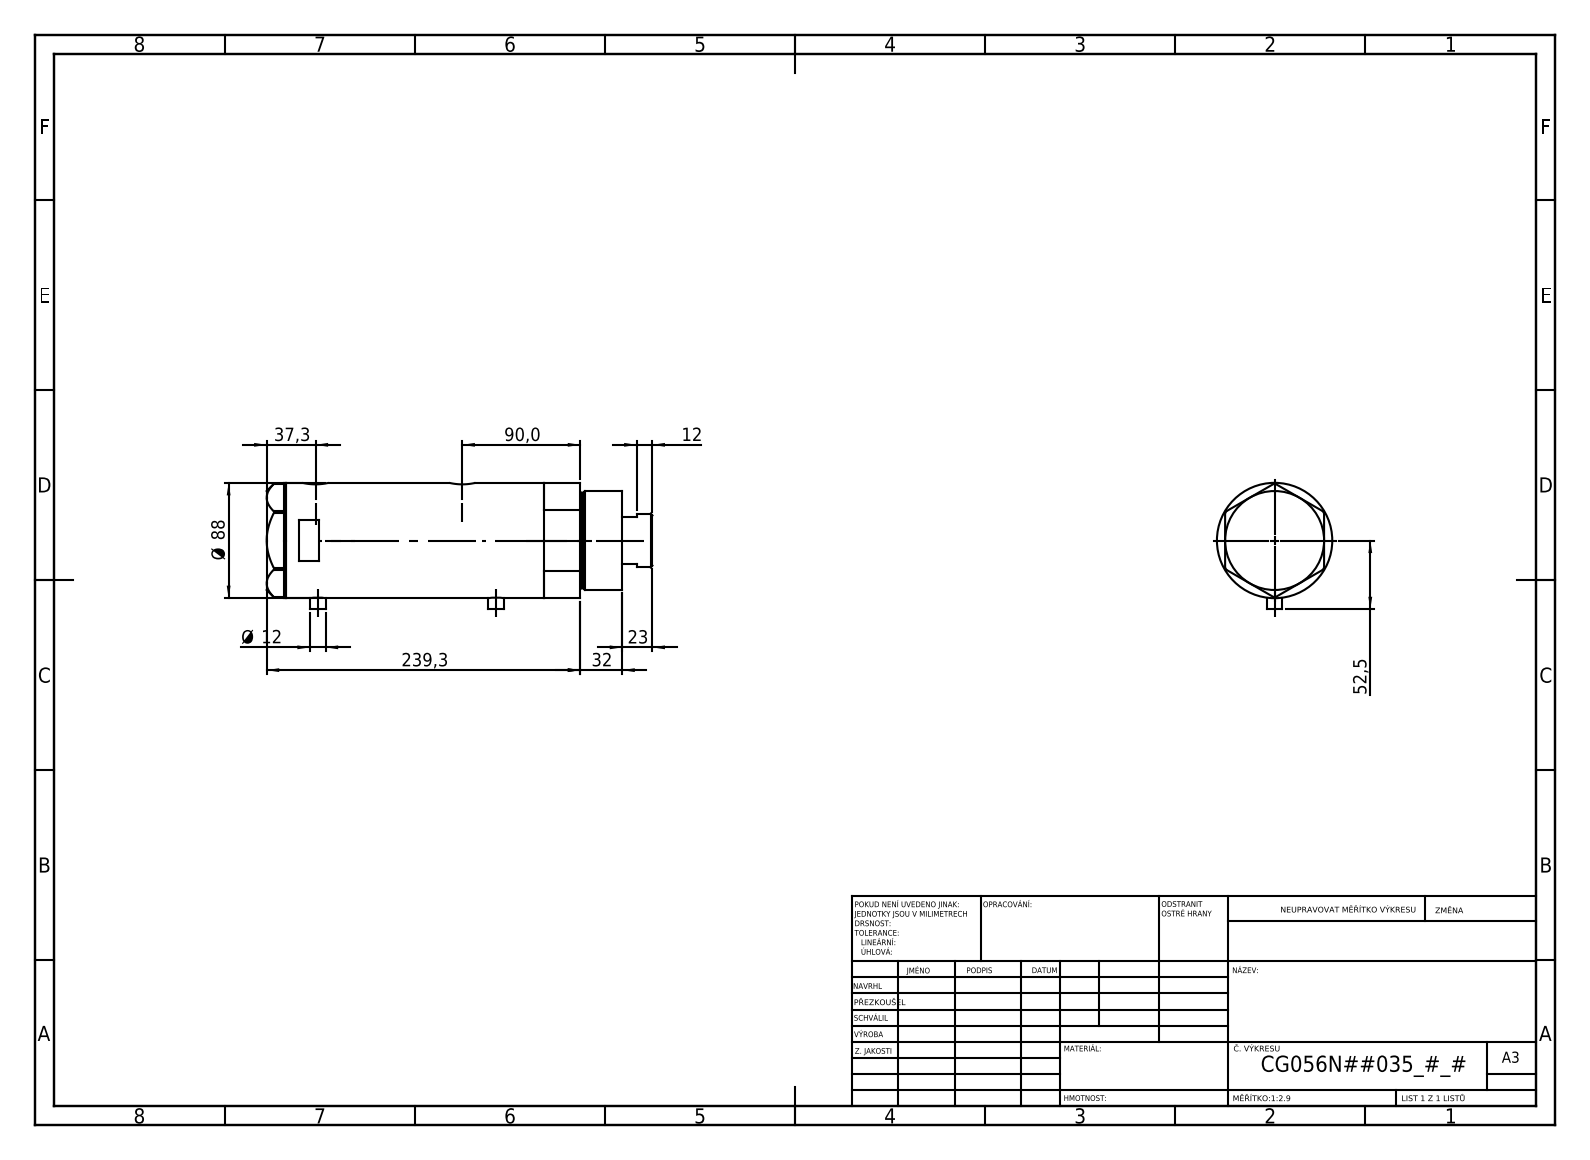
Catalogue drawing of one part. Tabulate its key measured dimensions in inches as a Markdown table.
| quantity | value |
| --- | --- |
| part name | V270CG_BACK; V270CG_VC; V270CG_MIDDLE; V270CG_FRONT |
| STEP written by | SolidWorks 2019 (CONFIG_CONTROL_DESIGN) |
| units | inches |
| bodies | 4 solids, 121 faces (52 planar, 49 cylindrical, 20 other) |
| overall size | 11.587 × 3.799 × 3.465 |
| volume | 94.59 in³ |
| surface area | 344.2 in² |
| round holes (diameter × count) | 0.492 × 2, 0.518 × 2, 0.787 × 2, 0.571 × 1, 1.654 × 1, 1.713 × 1, 2.205 × 1, 2.362 × 1, 3.15 × 1 |
| round bosses / shafts (diameter × count) | 0.472 × 2, 3.465 × 1, 2.953 × 1, 2.874 × 1, 1.614 × 1 |
| main face-to-face distances | 5.291, 1.024, 4.268, 0.591, 1.614, 5.882, 10.091, 10.681, 9.067, 4.799 |
| hole center spacings | 0.067, 1.016, 4.343, 4.409, 5.358, 5.425 |
